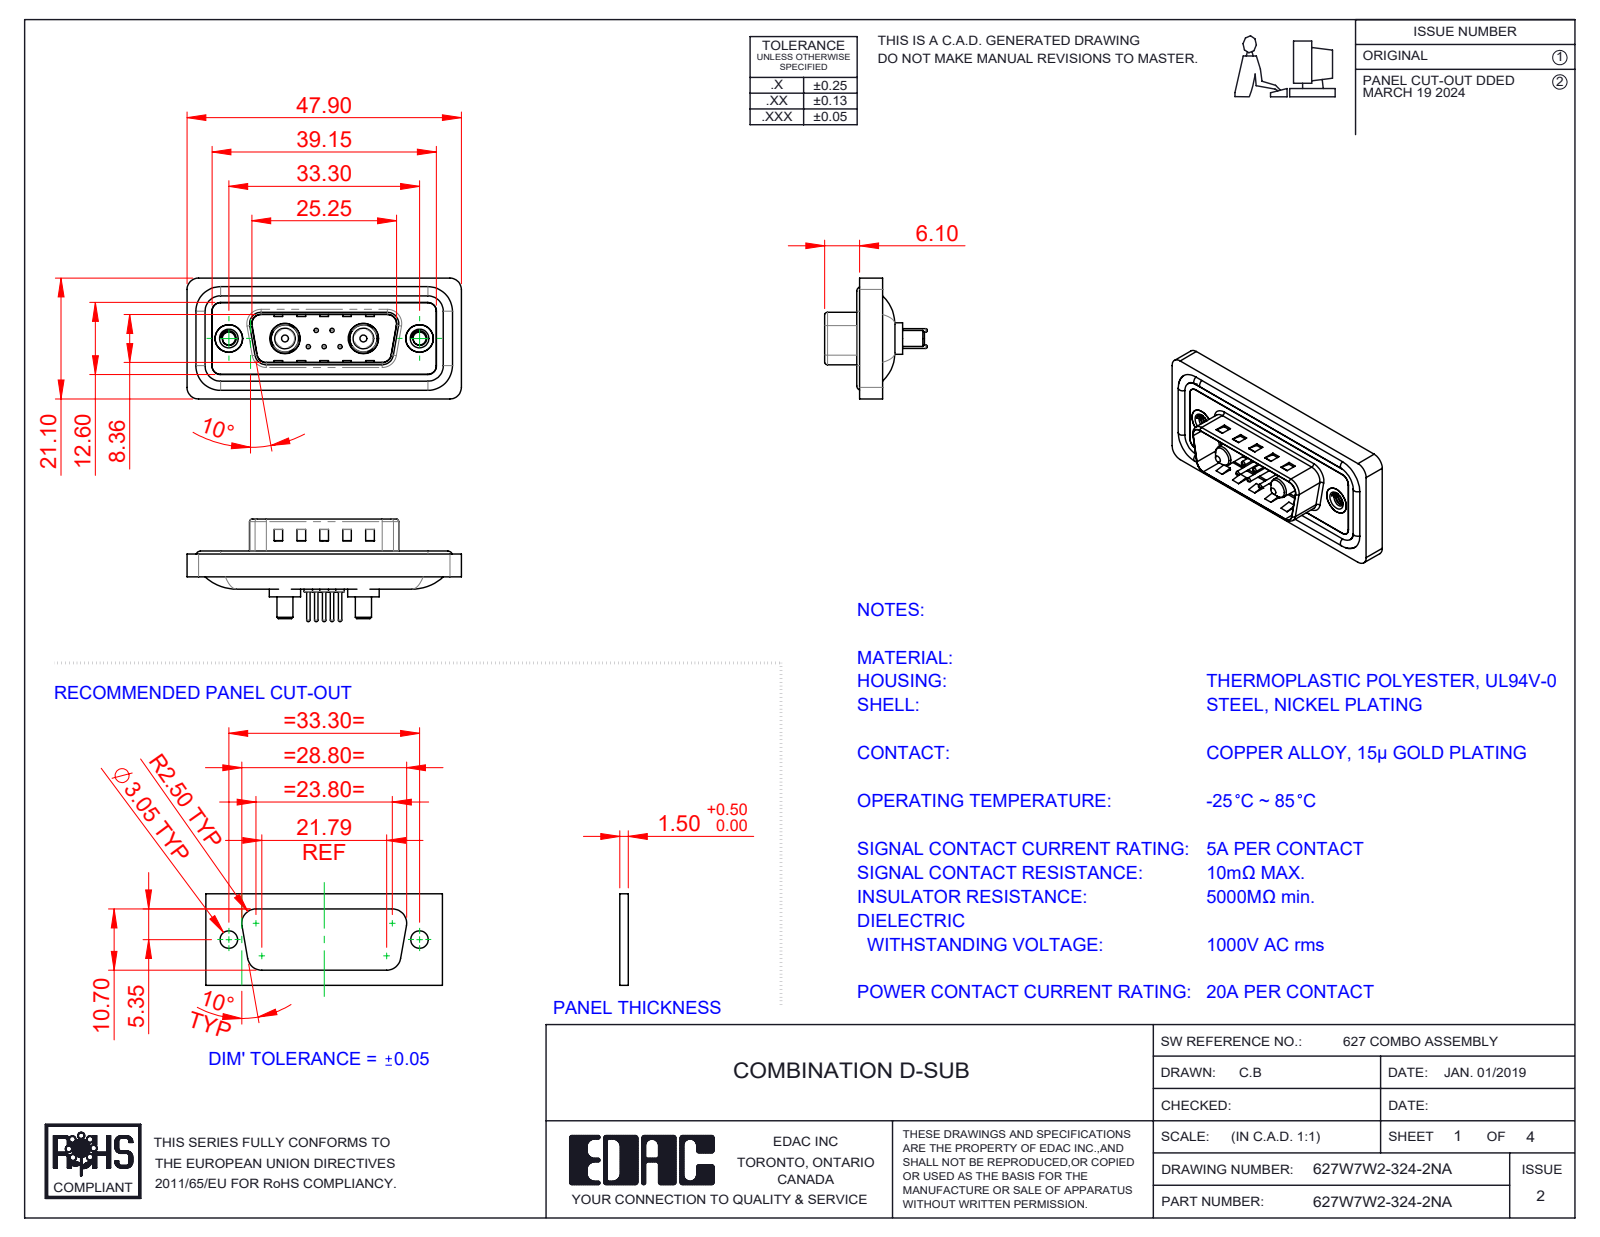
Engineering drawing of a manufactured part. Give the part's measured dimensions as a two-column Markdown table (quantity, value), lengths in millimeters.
| quantity | value |
| --- | --- |
| part name | 627Combo Housing_7W2; 627Combo Contact Row 1_24; 627Combo Shell Rear_15 Contacts; 627Combo Waterproof Housing_15 Contacts (+5 more) |
| STEP written by | SolidWorks 2023 (CONFIG_CONTROL_DESIGN) |
| units | millimeters |
| bodies | 16 solids, 708 faces (232 planar, 294 cylindrical, 182 other) |
| overall size | 47.9 × 21.1 × 17.9 |
| volume | 5 518 mm³ |
| surface area | 8 790 mm² |
| round holes (diameter × count) | 0.75 × 5, 1.6 × 5, 2 × 5, 2.26 × 2, 4 × 2, 4.8 × 2, 4.85 × 2, 5 × 2, 5.3 × 2 |
| round bosses / shafts (diameter × count) | 1.5 × 5, 0.6 × 5, 1.6 × 4, 5.5 × 2, 5.2 × 2, 4.9 × 2, 4.75 × 2, 3.75 × 2 |
| partial cylindrical surfaces (radius × count) | 1.5 × 26, 2 × 20, 0.5 × 8, 1.6 × 8, 0.25 × 4, 0.6 × 4, 0.65 × 4, 0.9 × 4 |
| main face-to-face distances | 0.4, 1.1, 1.5, 1.6, 0.5, 3.1, 2.9, 0.82, 9.58, 4 |
| hole center spacings | 3.16, 2.77, 9.8, 23.5, 4.31, 4.33, 5.03, 5.04 |
